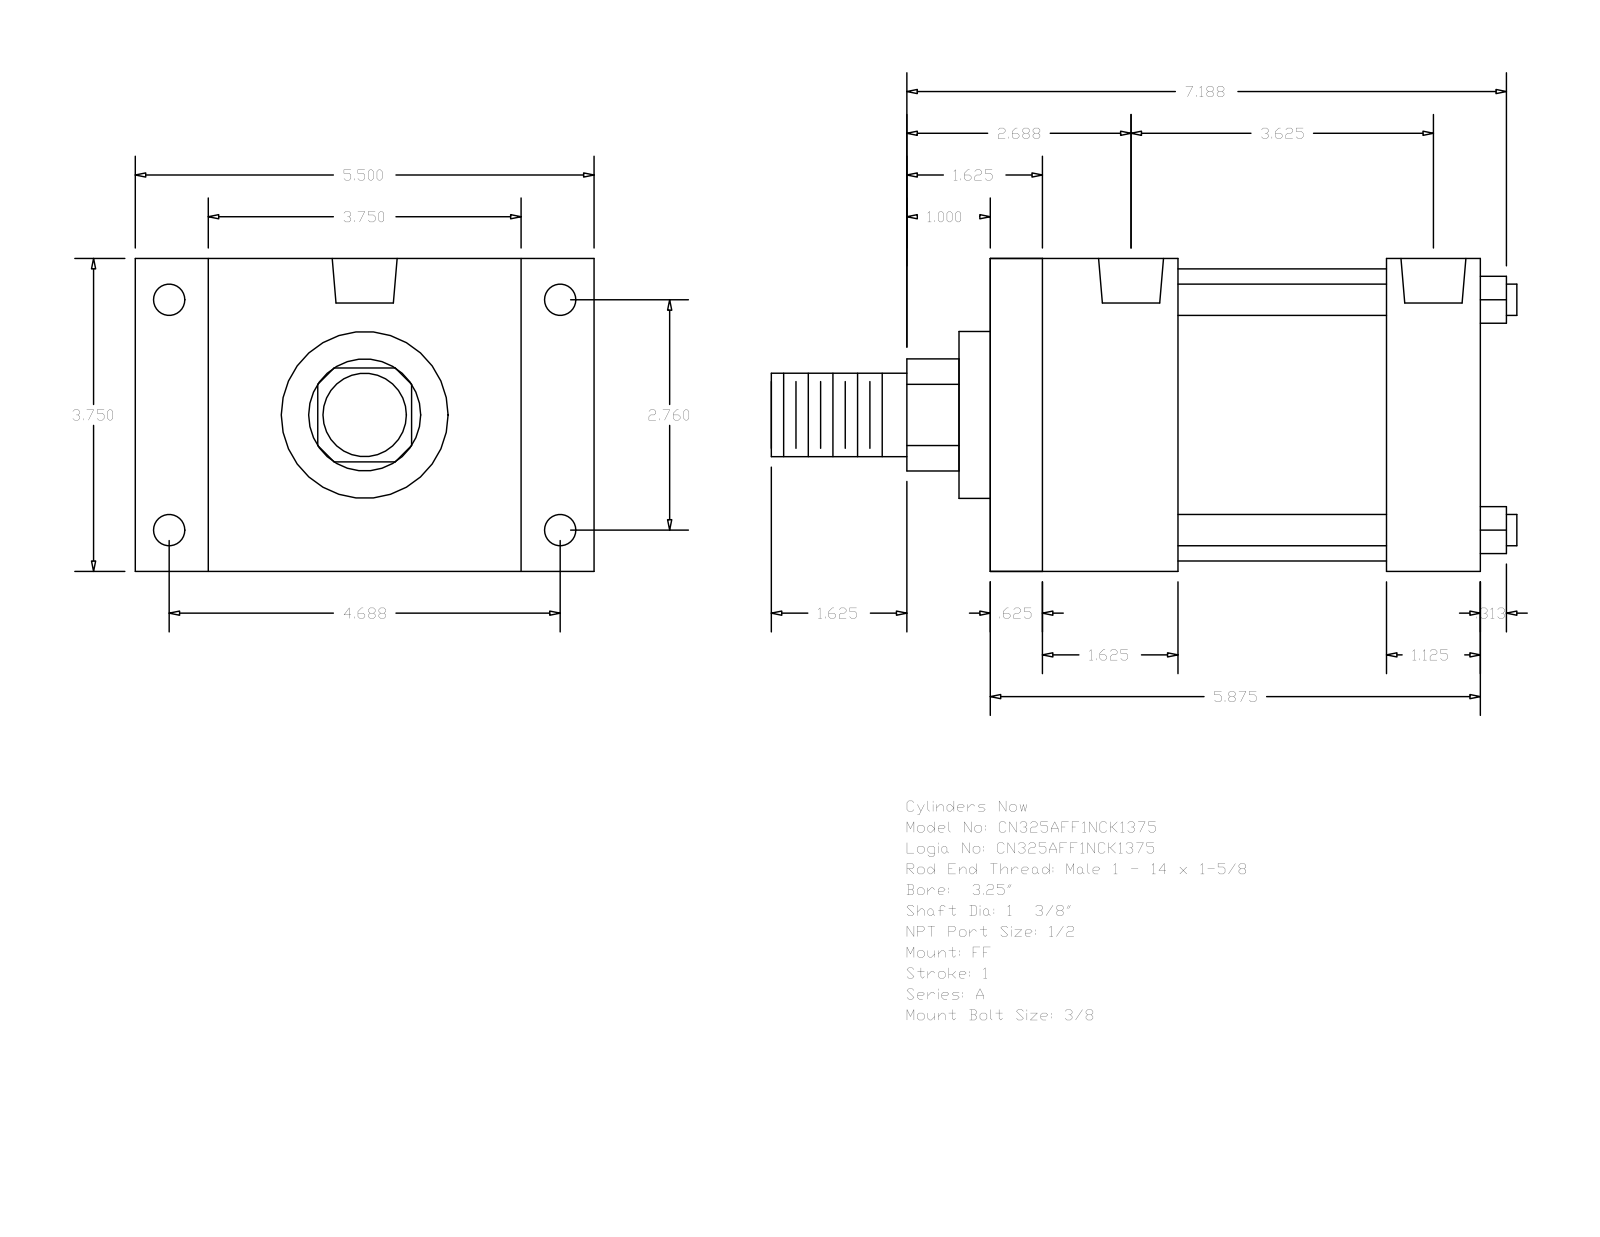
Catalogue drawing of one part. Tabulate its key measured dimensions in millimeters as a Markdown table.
| quantity | value |
| --- | --- |
| part name | A_FF__0325_1.375 |
| STEP written by | GSSL Pune (CONFIG_CONTROL_DESIGN) |
| units | millimeters |
| bodies | 0 solids, 92 faces (64 planar, 28 cylindrical, 0 other) |
| overall size | 227.01 × 139.7 × 95.25 |
| round holes (diameter × count) | 8.73 × 4, 9.53 × 4, 19.77 × 2 |
| round bosses / shafts (diameter × count) | 9.53 × 4, 88.9 × 1, 50.8 × 1, 34.92 × 1, 25.4 × 1 |
| partial cylindrical surfaces (radius × count) | 17.06 × 1 |
| main face-to-face distances | 95.24, 149.22, 133.35, 15.87, 57.15, 22.23, 117.47, 28.57, 120.65, 41.28 |
| hole center spacings | 3.18, 70.1, 85.72, 88.9, 119.06, 138.16, 92.08 |
